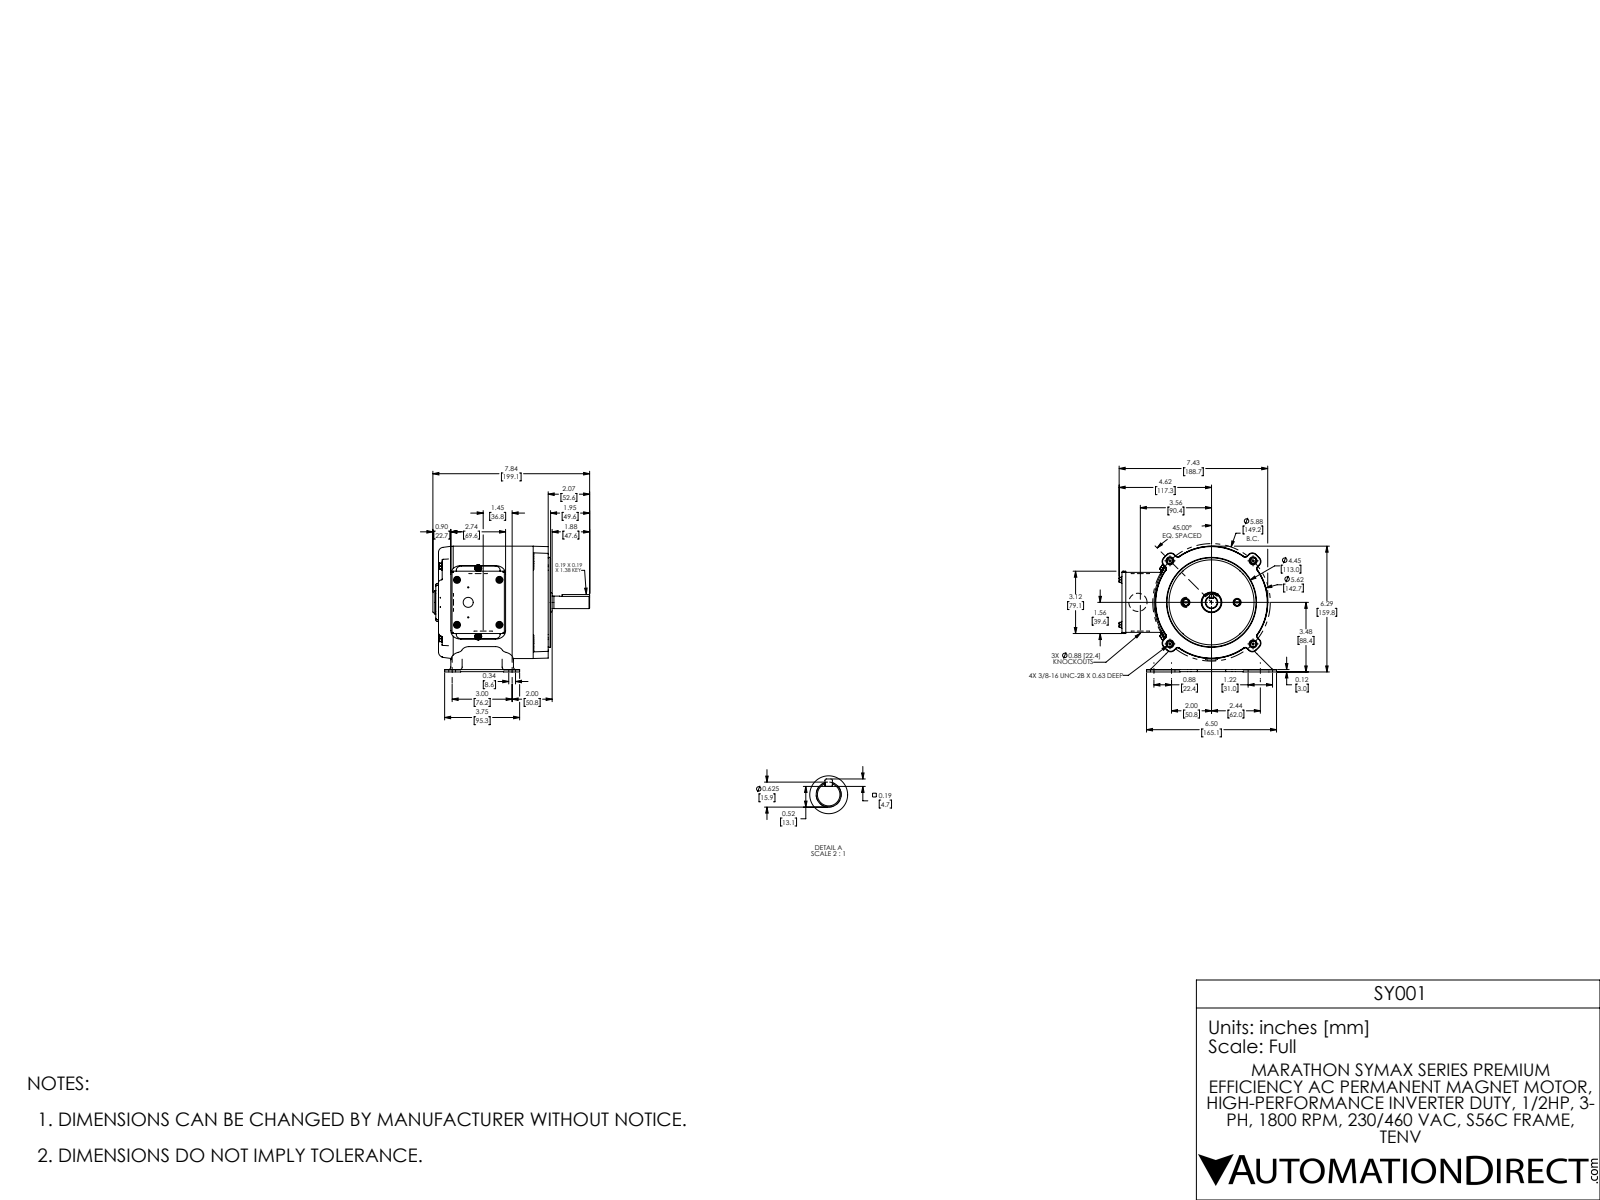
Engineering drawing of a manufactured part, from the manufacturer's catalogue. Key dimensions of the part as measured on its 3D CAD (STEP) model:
Part name (STEP PRODUCT): 614-0004-001_RevE_56CZ_0P5HP r1 coord
STEP written by: SolidWorks 2017 (AUTOMOTIVE_DESIGN)
Units: inches
Bodies: 25 solids, 4169 faces (1801 planar, 576 cylindrical, 1792 other)
Overall size (bounding box): 7.869 × 7.837 × 6.29
Volume: 28.42 in³ · Surface area: 536.8 in²
Round holes (diameter × count): ⌀0.22 ×6, ⌀0.19 ×5, ⌀0.06 ×4, ⌀0.136 ×4, ⌀0.201 ×4, ⌀0.25 ×4, ⌀0.88 ×3, ⌀0.154 ×2, ⌀0.226 ×2, ⌀0.28 ×2, ⌀0.5 ×1, ⌀0.67 ×1
Round bosses / shafts (diameter × count): ⌀0.399 ×6, ⌀0.348 ×6, ⌀0.19 ×6, ⌀0.164 ×6, ⌀0.166 ×4, ⌀0.91 ×3, ⌀5.62 ×1, ⌀5.497 ×1
Partial cylindrical surfaces — rounded edges, fillets, slot ends (radius × count): R0.06 ×54, R0.045 ×40, R0.03 ×32, R0.13 ×22, R0.17 ×18, R0.25 ×14, R0.16 ×12, R0.38 ×12
Main face-to-face distances: 0.048, 0.09, 5.485, 5.395, 0.104, 2.452, 0.015, 2.952, 4.75, 0.13
Hole centre spacings: 2.12, 3.091, 1.893, 2.25, 2.562, 3.624, 4.548, 0.75
